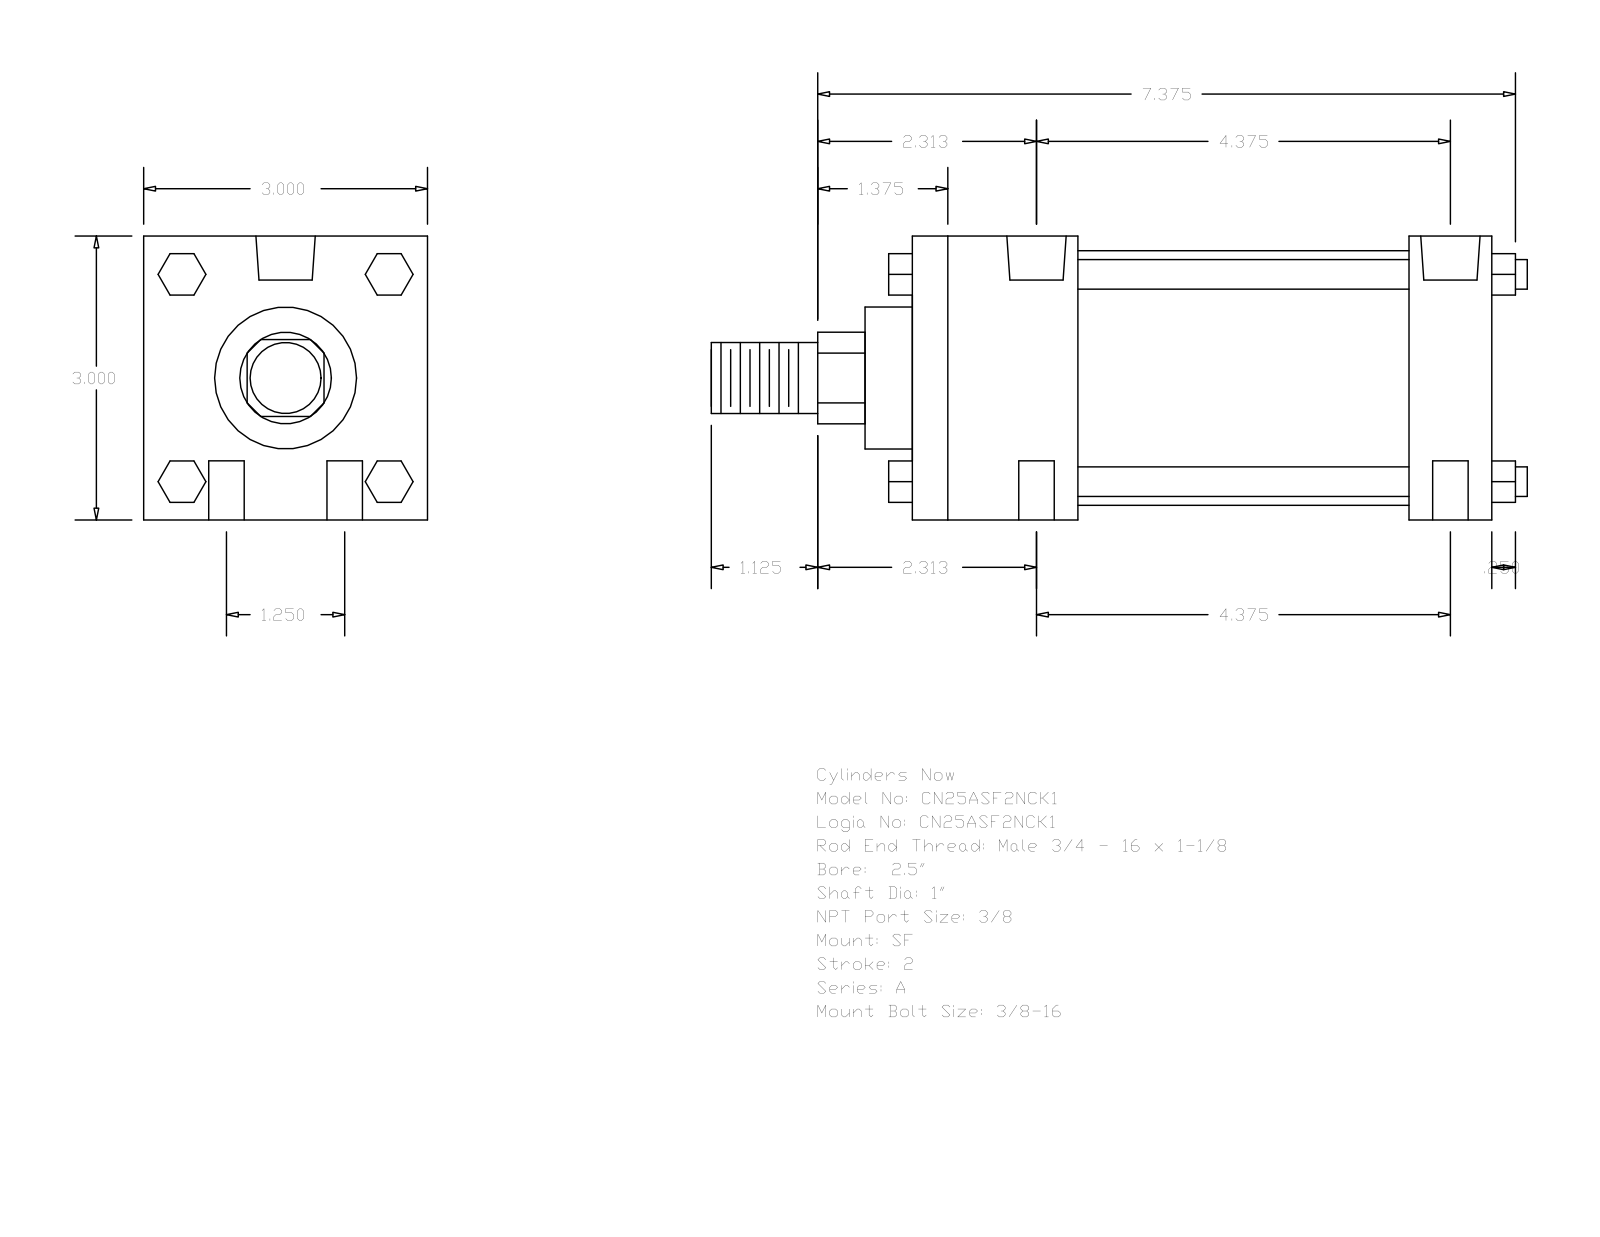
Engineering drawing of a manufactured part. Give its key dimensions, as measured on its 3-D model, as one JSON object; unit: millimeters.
{"part_name": "A_SF__0250_1", "step_written_by": "GSSL Pune (CONFIG_CONTROL_DESIGN)", "units": "millimeters", "bodies": {"solids": 0, "faces": 124, "planar": 94, "cylindrical": 30, "other": 0}, "overall_size": [219.07, 76.2, 76.2], "round_holes": [[9.53, 4], [5.56, 2], [15.93, 2]], "round_bosses_or_shafts": [[7.94, 4], [68.33, 1], [38.1, 1], [25.4, 1], [19.05, 1]], "partial_cylinders_radius": [[12.29, 1]], "face_to_face_distances": [76.2, 155.57, 133.35, 22.22, 44.45, 88.9, 111.12, 12.7, 168.27, 6.35], "hole_center_spacings": [15.88, 112.25, 111.12, 31.76, 115.57, 115.88]}
